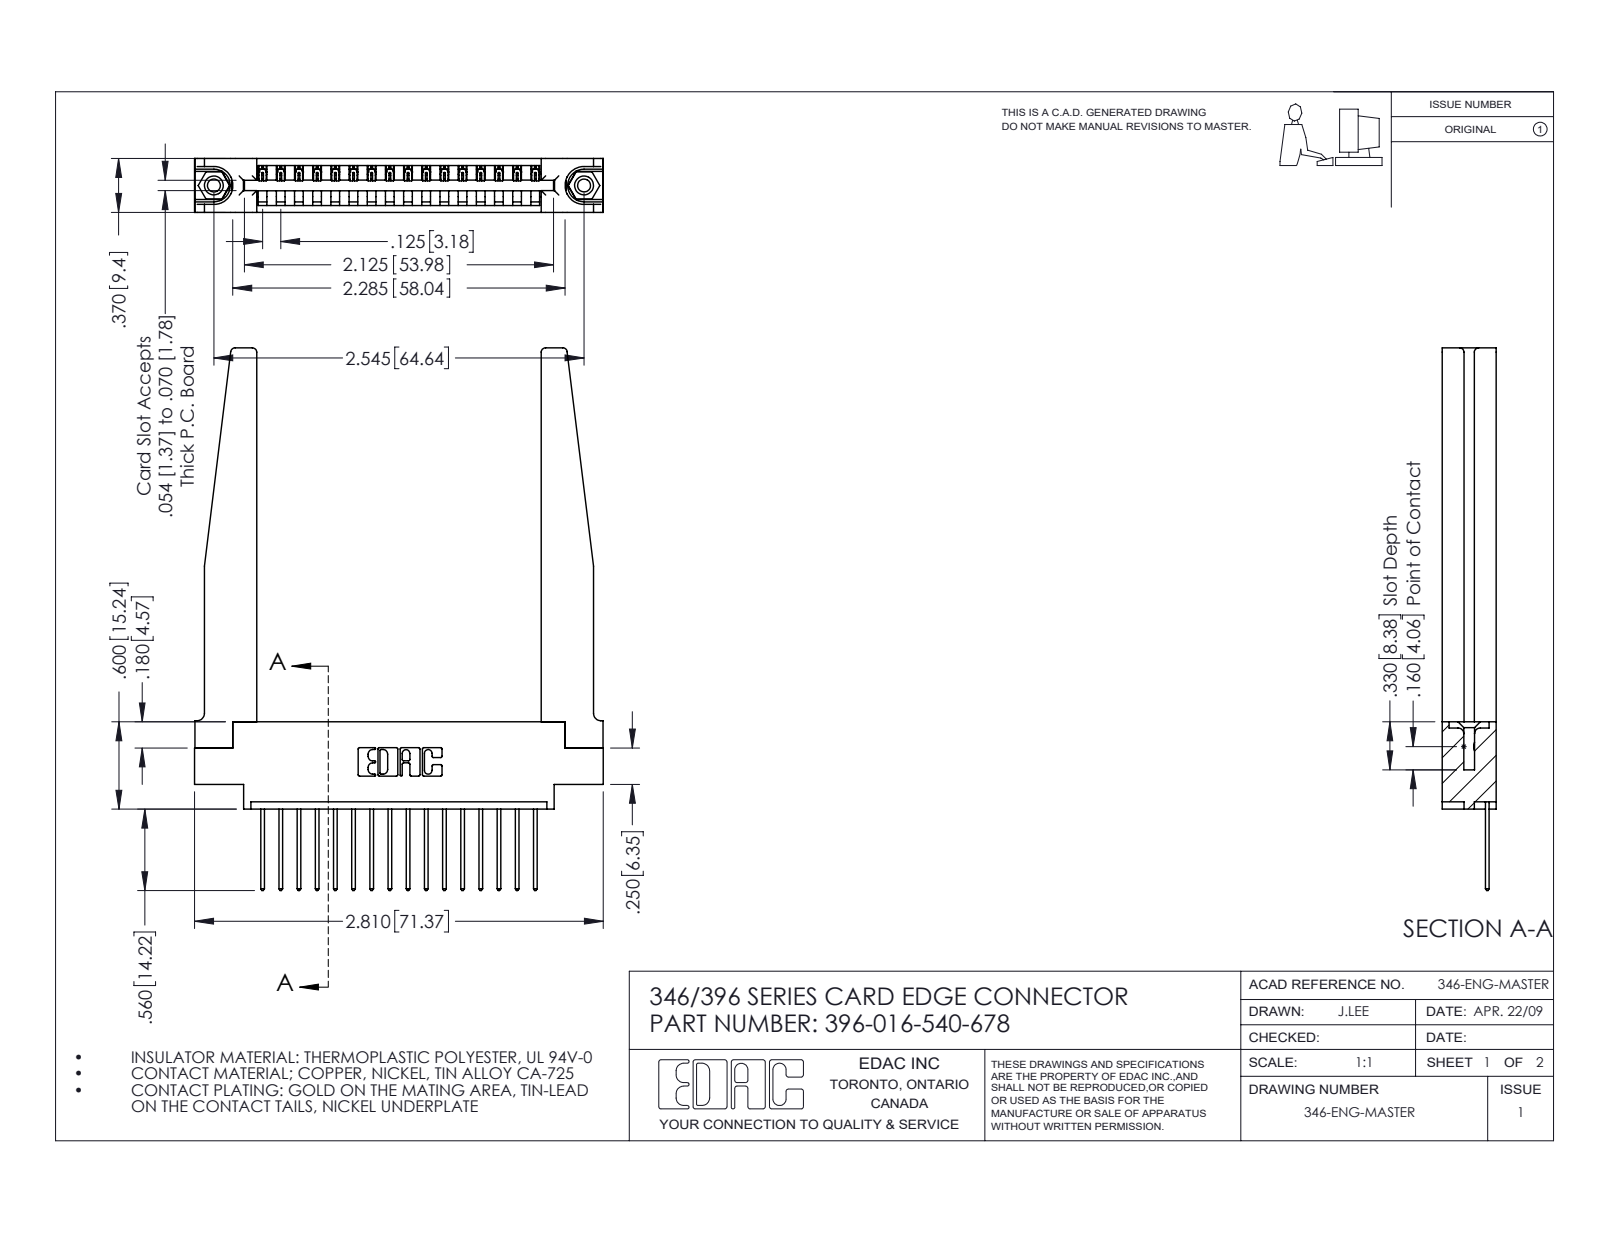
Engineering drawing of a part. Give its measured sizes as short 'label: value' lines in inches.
name: 346-220-078_345-220-078; 396-016-540-678; 345-250-001_345-250-001-102; 346 Part_0.170 Offset - 0.156 Dia-TH (+1 more)
written by: SolidWorks 2016 (CONFIG_CONTROL_DESIGN)
unit: in
bodies: 21 solids, 1288 faces (862 planar, 374 cylindrical, 52 other)
size: 3.73 × 2.81 × 0.37
volume: 0.819 in³; area: 22.83 in²
holes: 2× ⌀0.089, 2× ⌀0.125, 2× ⌀0.156, 1× ⌀0.064
bosses: 2× ⌀0.155
rounds: 32× R0.006, 32× R0.01, 22× R0.01, 8× R0.03, 6× R0.007, 6× R0.031, 3× R0.026, 2× R0.031
face distances: 0.37, 0.072, 0.15, 0.048, 0.322, 0.148, 0.25, 0.298, 0.025, 0.102
hole spacings: 0.246, 2.338, 2.545
